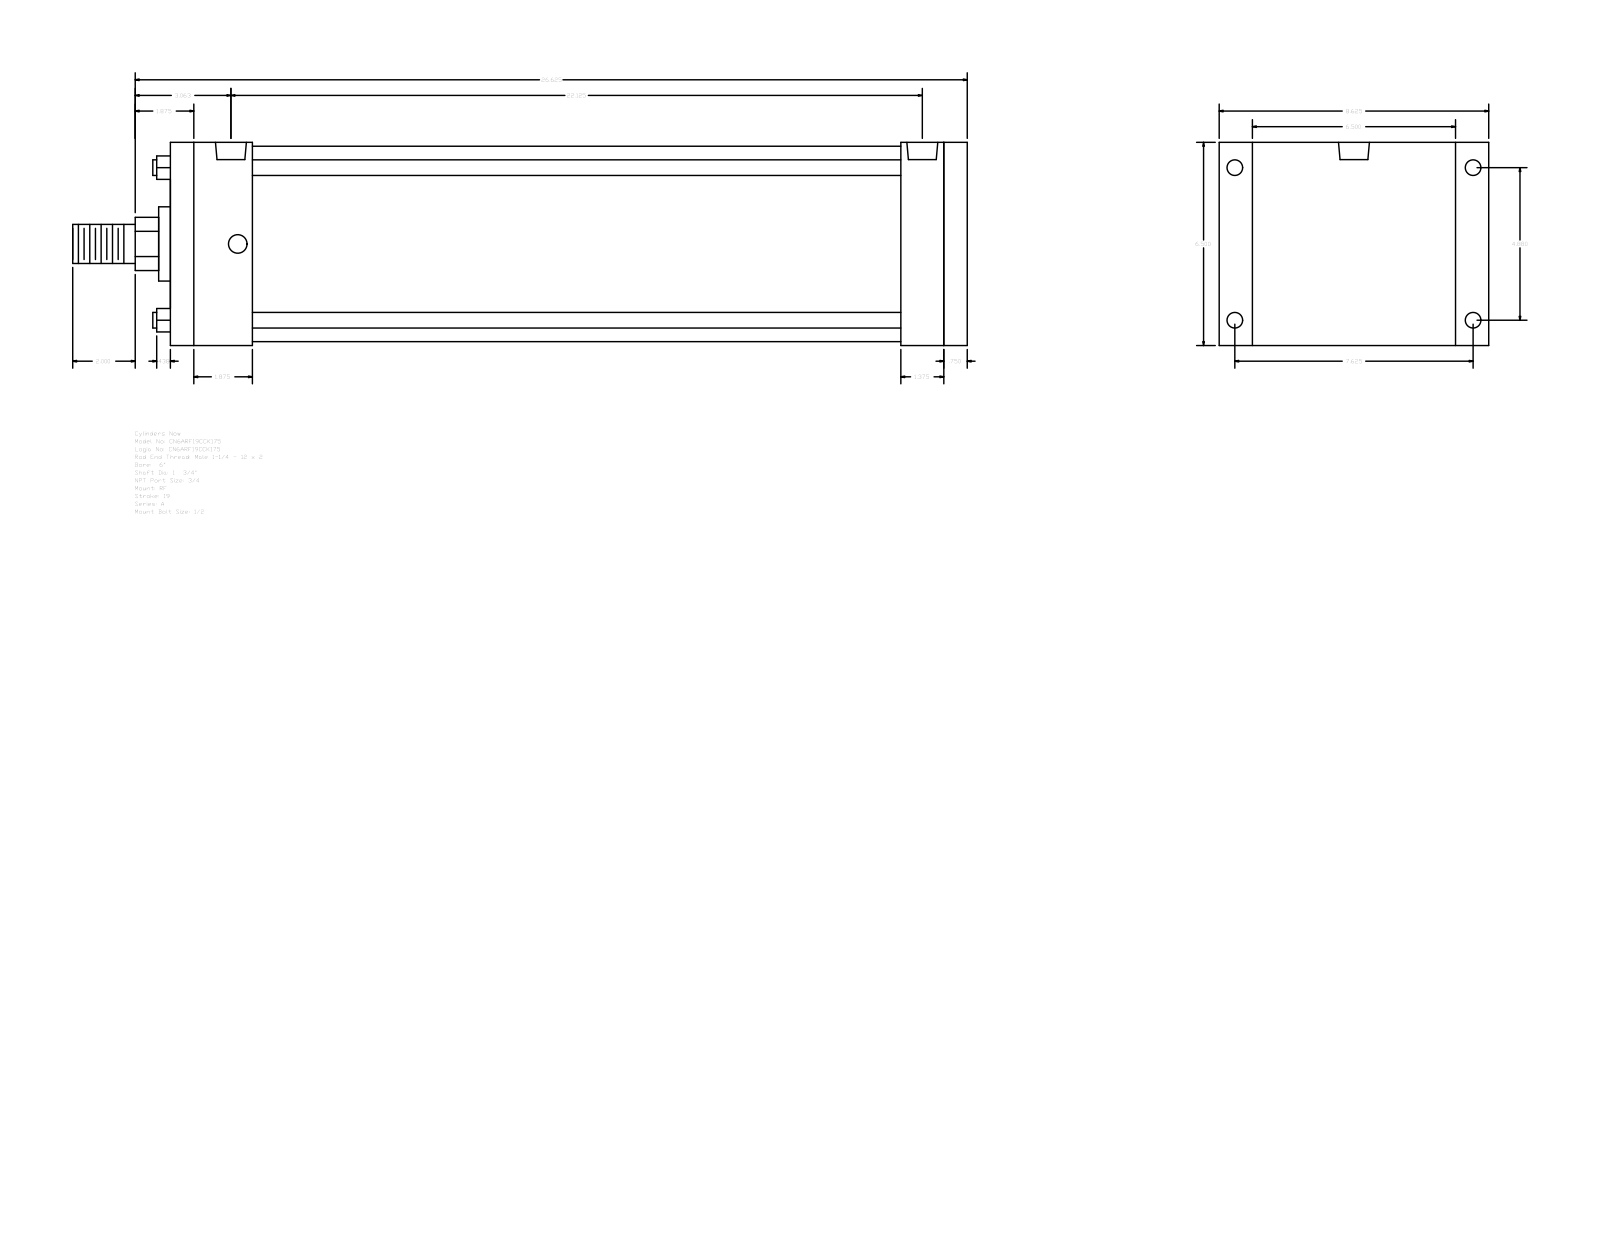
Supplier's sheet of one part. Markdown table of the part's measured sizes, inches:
| quantity | value |
| --- | --- |
| part name | A_RF__0600_1.75 |
| STEP written by | GSSL Pune (CONFIG_CONTROL_DESIGN) |
| units | inches |
| bodies | 0 solids, 92 faces (64 planar, 28 cylindrical, 0 other) |
| overall size | 28.625 × 8.625 × 6.5 |
| round holes (diameter × count) | 0.5 × 4, 0.594 × 4, 0.989 × 2 |
| round bosses / shafts (diameter × count) | 0.5 × 4, 6.25 × 1, 2.375 × 1, 1.75 × 1, 1.25 × 1 |
| partial cylindrical surfaces (radius × count) | 0.852 × 1 |
| main face-to-face distances | 6.5, 25.5, 24.75, 0.75, 2.625, 22.125, 22.875, 23.375, 20.75, 1.375 |
| hole center spacings | 0.219, 4.88, 7.625, 9.053, 21.687, 21.906, 22.125 |
